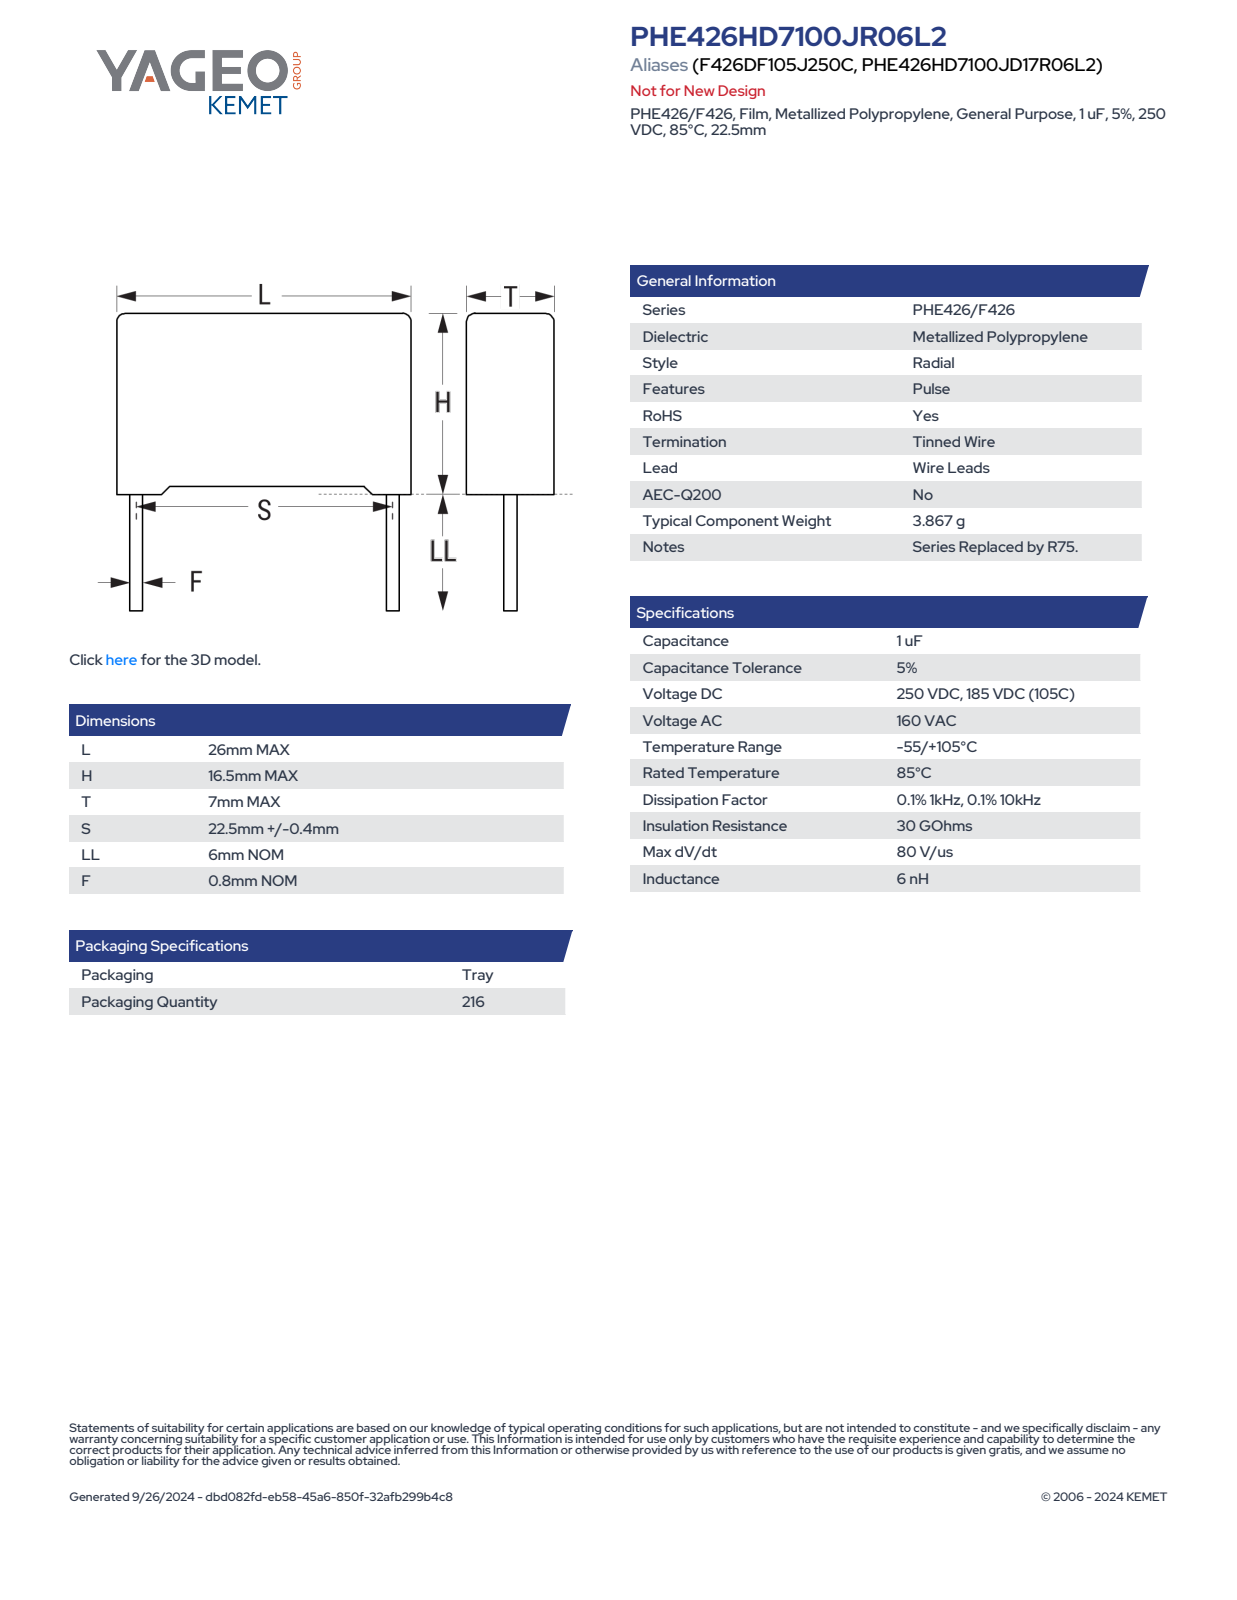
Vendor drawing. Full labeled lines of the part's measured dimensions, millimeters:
Part name (STEP PRODUCT): CFR_RB2_26X16.5X7_L26H16.5T7S22.5LL6F0.8
STEP written by: SolidWorks 2021 (AUTOMOTIVE_DESIGN)
Units: millimetres
Bodies: 4 solids, 85 faces (77 planar, 8 cylindrical, 0 other)
Overall size (bounding box): 26 × 22.5 × 7
Volume: 2 892 mm³ · Surface area: 1 526 mm²
Round bosses / shafts (diameter × count): ⌀0.8 ×2
Partial cylindrical surfaces — rounded edges, fillets, slot ends (radius × count): R0.5 ×4
Main face-to-face distances: 7, 15.75, 26, 15.93, 0.87, 0.57, 0.75, 16.5, 6.13, 25.13
